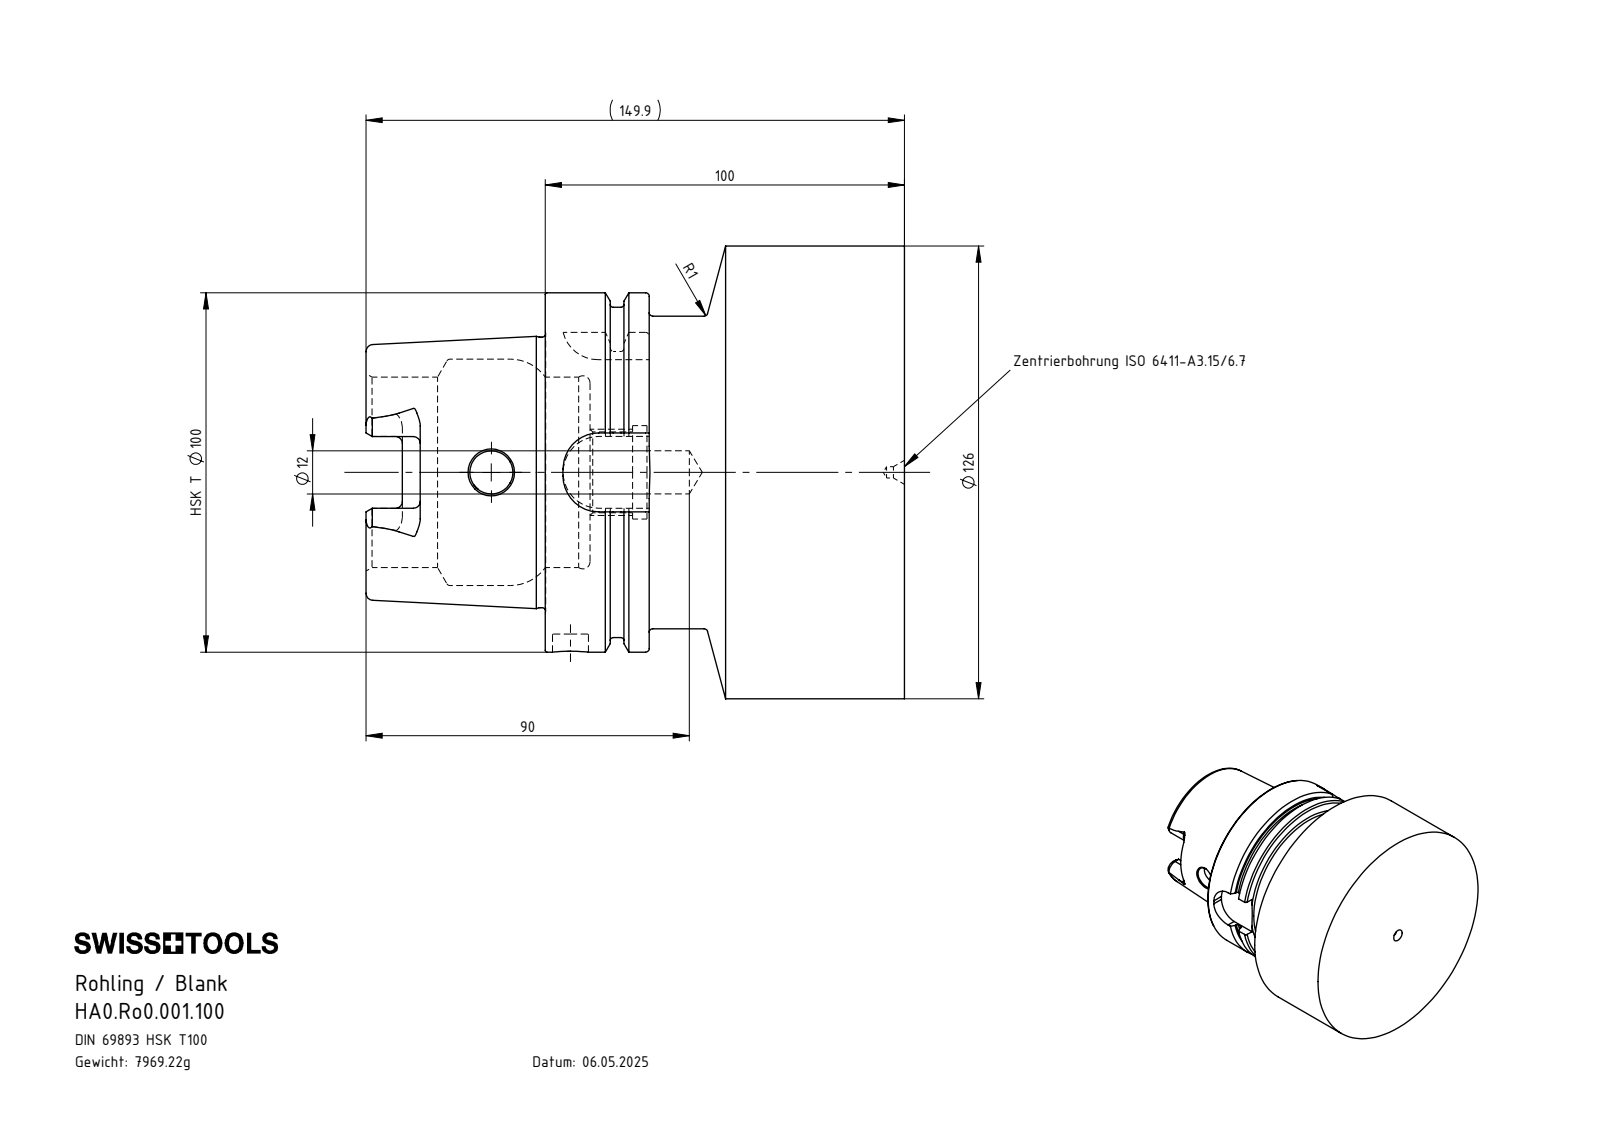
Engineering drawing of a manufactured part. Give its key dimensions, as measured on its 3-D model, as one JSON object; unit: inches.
{"part_name": "HA0.Ro0.001.100", "step_written_by": "SolidWorks 2022 (AUTOMOTIVE_DESIGN)", "units": "inches", "bodies": {"solids": 1, "faces": 159, "planar": 38, "cylindrical": 50, "other": 71}, "overall_size": [5.902, 4.961, 4.961], "volume_in3": 61.94, "surface_area_in2": 135.4, "round_holes": [[0.472, 2], [0.124, 1], [0.394, 1], [0.886, 1], [1.024, 1], [2.087, 1], [2.48, 1]], "round_bosses_or_shafts": [[4.961, 1], [3.937, 1], [3.62, 1], [3.425, 1], [2.963, 1]], "partial_cylinders_radius": [[0.075, 6], [0.192, 4], [0.394, 4]], "face_to_face_distances": [3.937, 0.49, 3.447, 1.14, 0.65, 2.797, 1.965, 2.455, 3.104, 5.902]}
